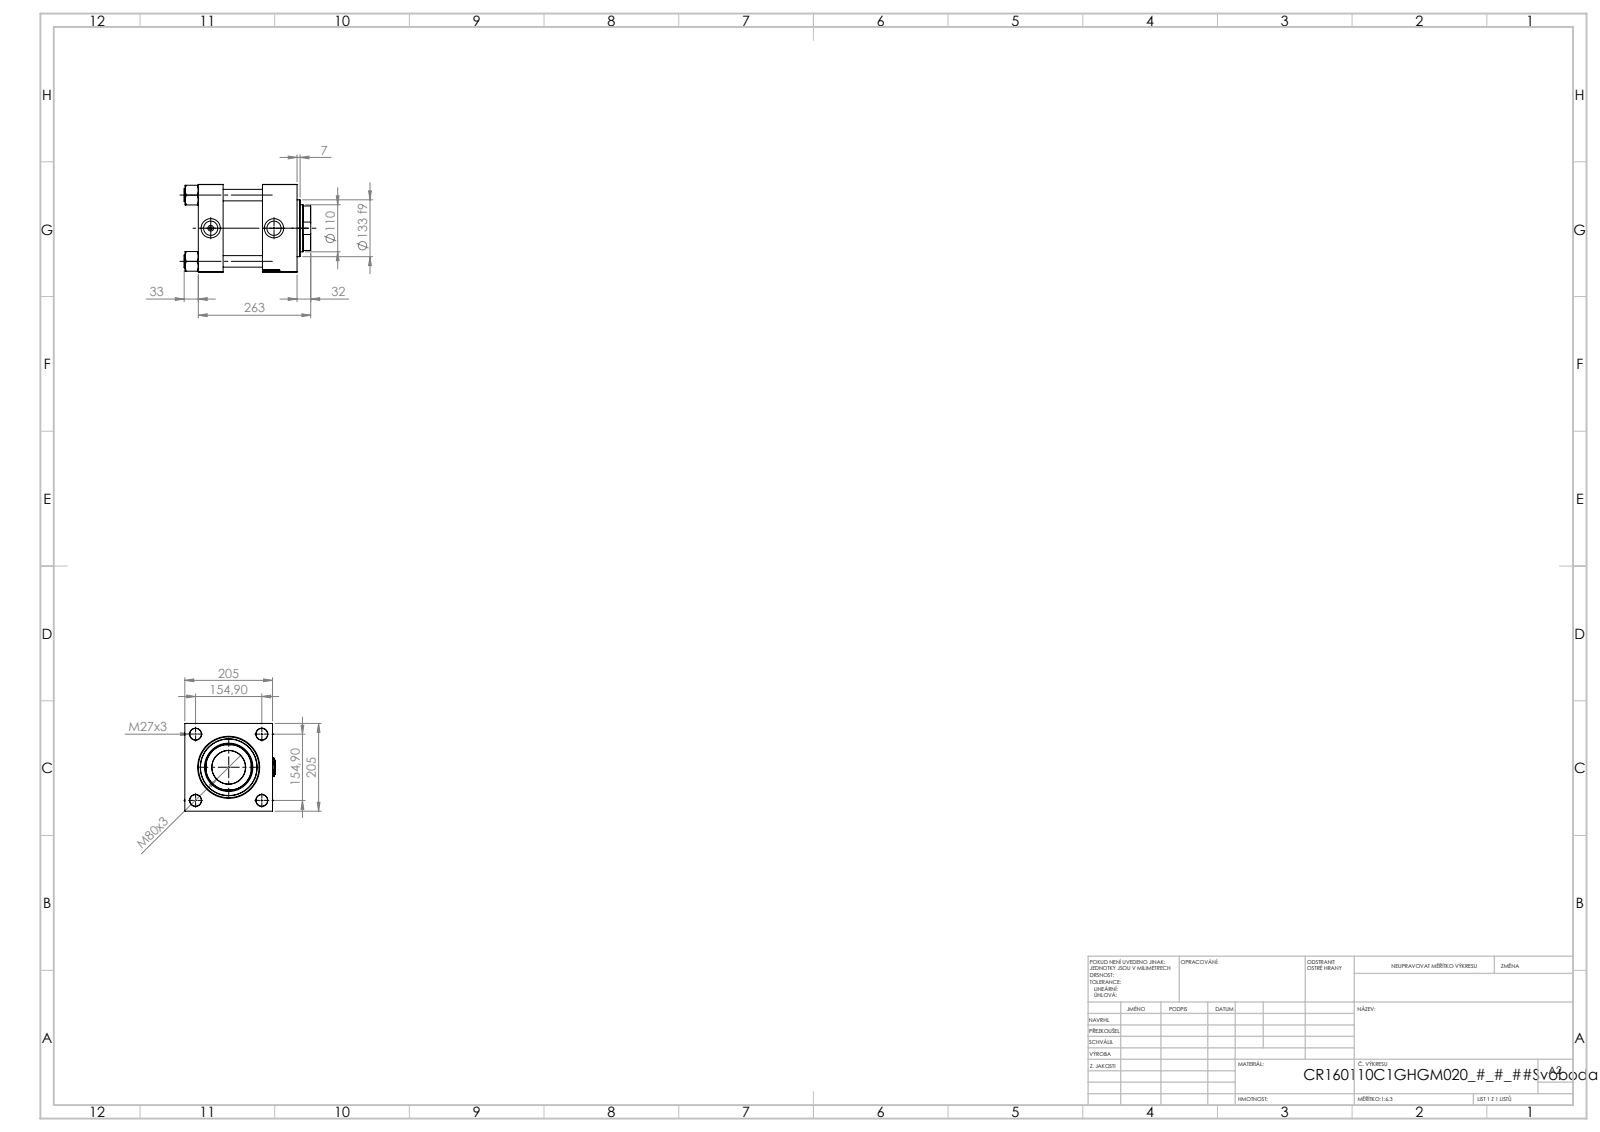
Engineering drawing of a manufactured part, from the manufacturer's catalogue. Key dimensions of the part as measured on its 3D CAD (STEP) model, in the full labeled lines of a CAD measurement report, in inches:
Part name (STEP PRODUCT): V215CR_VCP_C; NUT_M5_C; V215CR_C_TYCINKA; V215CR_C_Body (+2 more)
STEP written by: SolidWorks 2019 (CONFIG_CONTROL_DESIGN)
Units: inches
Bodies: 12 solids, 1243 faces (597 planar, 90 cylindrical, 556 other)
Overall size (bounding box): 11.654 × 8.408 × 8.071
Volume: 465.1 in³ · Surface area: 1 126 in²
Round holes (diameter × count): ⌀1.063 ×4, ⌀0.276 ×2, ⌀1.309 ×2, ⌀1.772 ×2, ⌀3.091 ×1, ⌀4.331 ×1, ⌀4.449 ×1, ⌀4.724 ×1, ⌀5.591 ×1, ⌀6.299 ×1
Round bosses / shafts (diameter × count): ⌀1.181 ×4, ⌀6.535 ×1, ⌀5.236 ×1
Partial cylindrical surfaces — rounded edges, fillets, slot ends (radius × count): R2.126 ×1
Main face-to-face distances: 8.071, 2.283, 5.906, 3.622, 9.094, 6.811, 3.189, 7.965, 5.681, 2.059
Hole centre spacings: 4.312, 6.098, 8.624, 5.827
